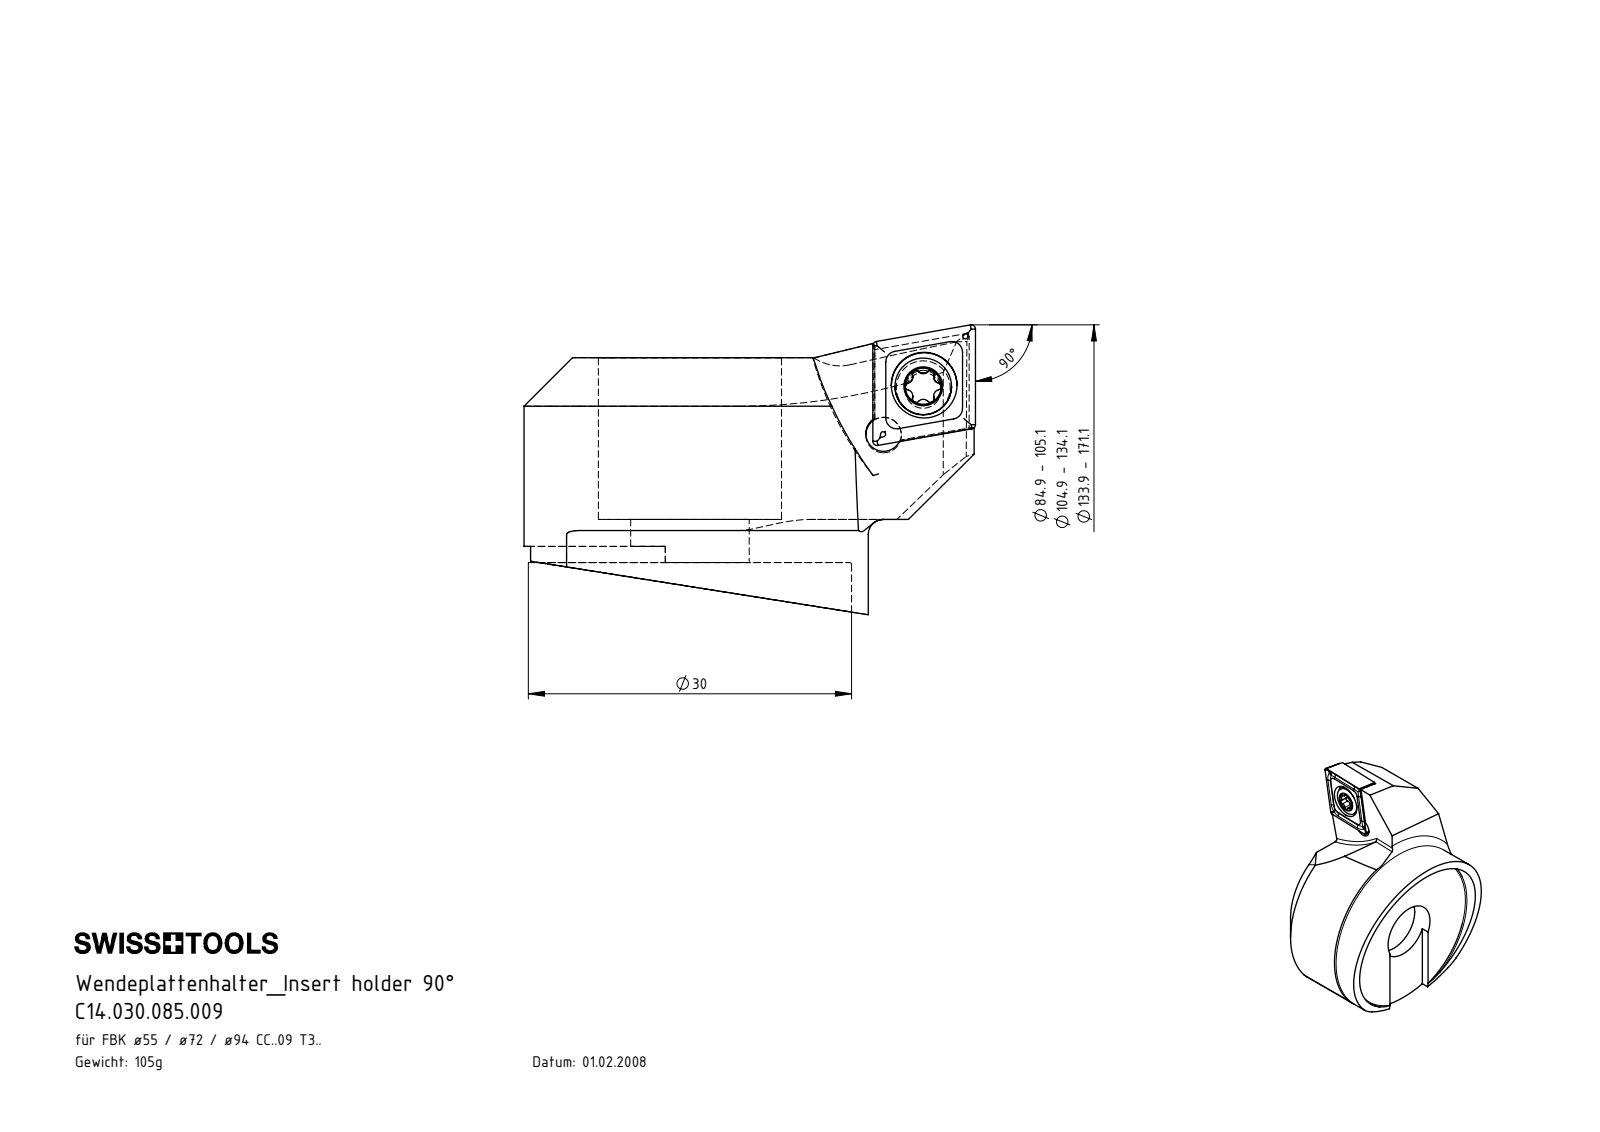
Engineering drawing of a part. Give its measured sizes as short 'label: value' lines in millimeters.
name: F55-WCB.001.022_D_fertigbearbeitet; WCB-ER2.001.009_A; CCMT09T304; C14.030.085.009
written by: SolidWorks 2017 (CONFIG_CONTROL_DESIGN)
unit: mm
bodies: 5 solids, 164 faces (50 planar, 51 cylindrical, 63 other)
size: 41.9 × 33.2 × 26.89
volume: 13 868 mm³; area: 6 463 mm²
holes: 2× ⌀3.3, 1× ⌀4.4, 1× ⌀6.1, 1× ⌀11, 1× ⌀17, 1× ⌀30
bosses: 1× ⌀5.25, 1× ⌀4
rounds: 6× R0.34, 6× R0.59, 2× R0.5, 2× R10, 1× R1.65, 1× R5, 1× R16.55, 1× R16.6
face distances: 19, 1, 18, 15, 14, 4, 3.77, 17.5, 16.5, 2.5
hole spacings: 5.73, 5.86
